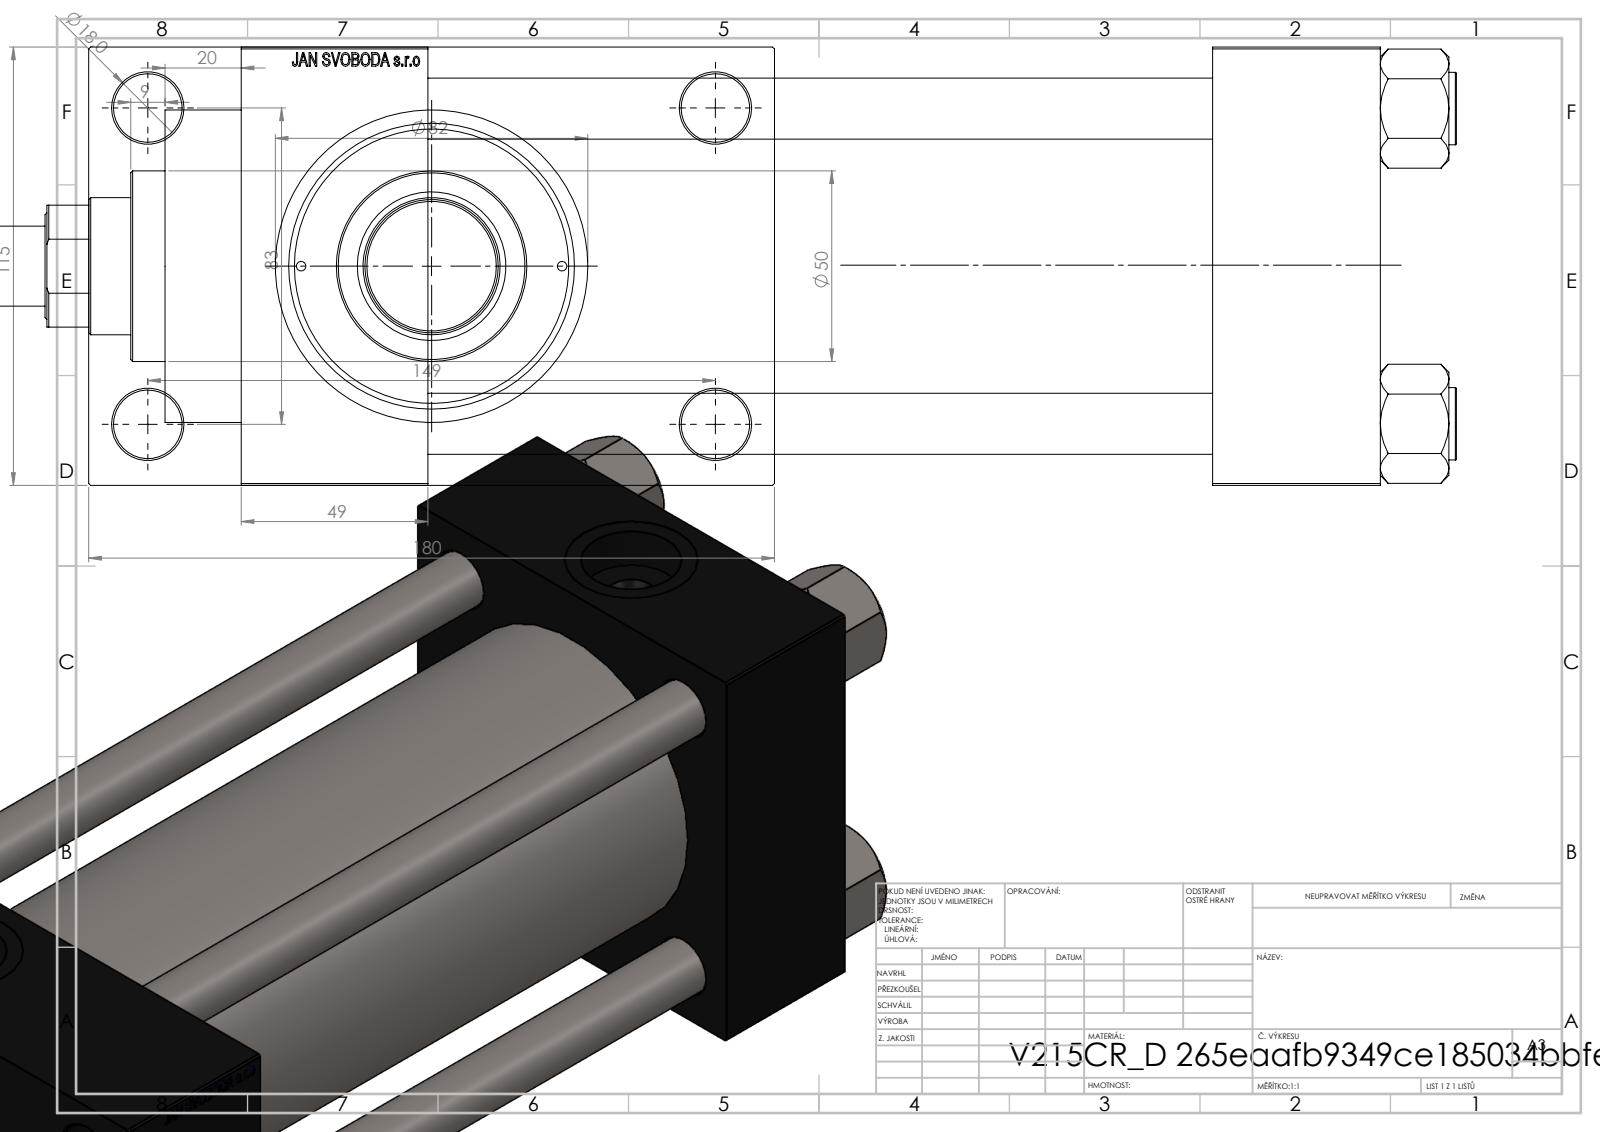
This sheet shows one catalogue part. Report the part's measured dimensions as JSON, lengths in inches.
{"part_name": "V215CR_D_Body; V215CR_VCP_D; V215CR_D_TYCINKA; NUT_M5_D (+2 more)", "step_written_by": "SolidWorks 2019 (CONFIG_CONTROL_DESIGN)", "units": "inches", "bodies": {"solids": 12, "faces": 1174, "planar": 551, "cylindrical": 97, "other": 526}, "overall_size": [15.984, 7.087, 4.528], "volume_in3": 145.5, "surface_area_in2": 645.3, "round_holes": [[0.63, 4], [0.709, 4], [0.098, 2], [0.276, 2], [1.041, 2], [1.378, 2], [1.004, 1], [1.417, 1], [1.535, 1], [2.402, 1], [2.835, 1], [3.15, 1]], "round_bosses_or_shafts": [[0.748, 4], [3.386, 1], [3.228, 1], [1.969, 1], [1.378, 1], [0.827, 1]], "face_to_face_distances": [4.528, 8.11, 1.929, 10.039, 1.732, 9.843, 11.772, 1.28, 5.807, 7.087], "hole_center_spacings": [1.305, 1.652, 2.276, 2.302, 3.256, 3.357, 3.393, 3.513]}
